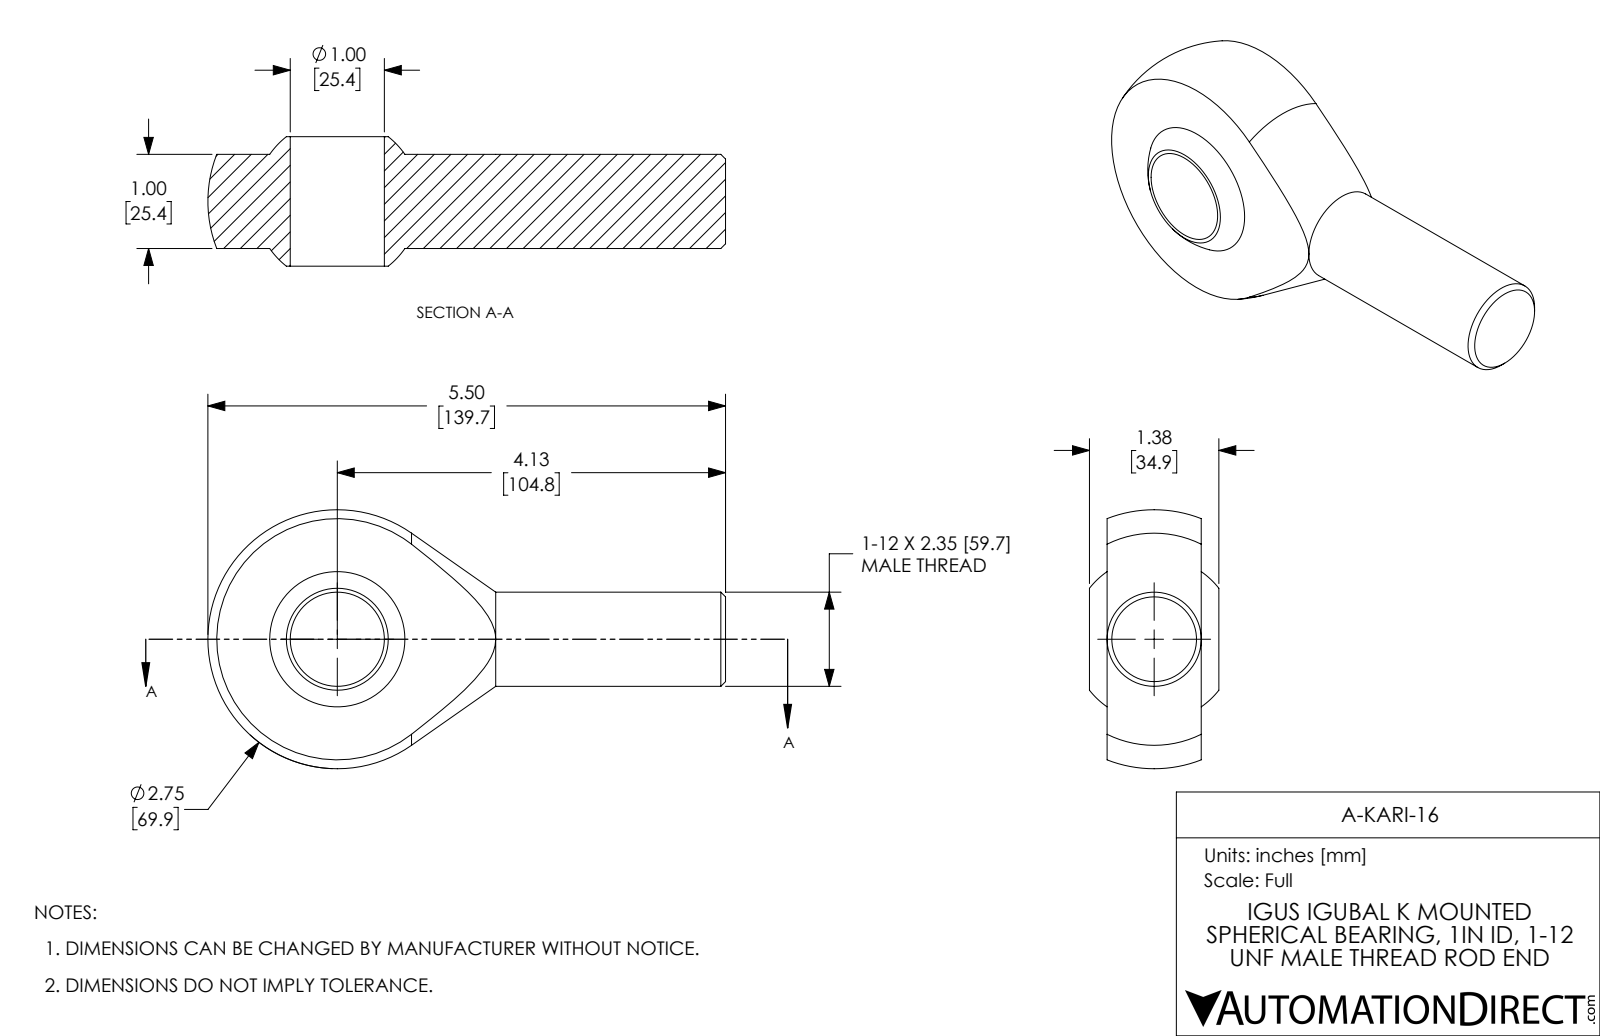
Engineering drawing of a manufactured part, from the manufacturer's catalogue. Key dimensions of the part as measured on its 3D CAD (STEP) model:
Part name (STEP PRODUCT): A-KARI-16
STEP written by: SolidWorks 2017 (AUTOMOTIVE_DESIGN)
Units: inches
Bodies: 1 solid, 20 faces (5 planar, 4 cylindrical, 11 other)
Overall size (bounding box): 5.445 × 2.75 × 1.375
Volume: 7.495 in³ · Surface area: 31.38 in²
Round holes (diameter × count): ⌀1 ×1
Round bosses / shafts (diameter × count): ⌀1 ×1
Main face-to-face distances: 1, 0.187, 1.187, 1.375
